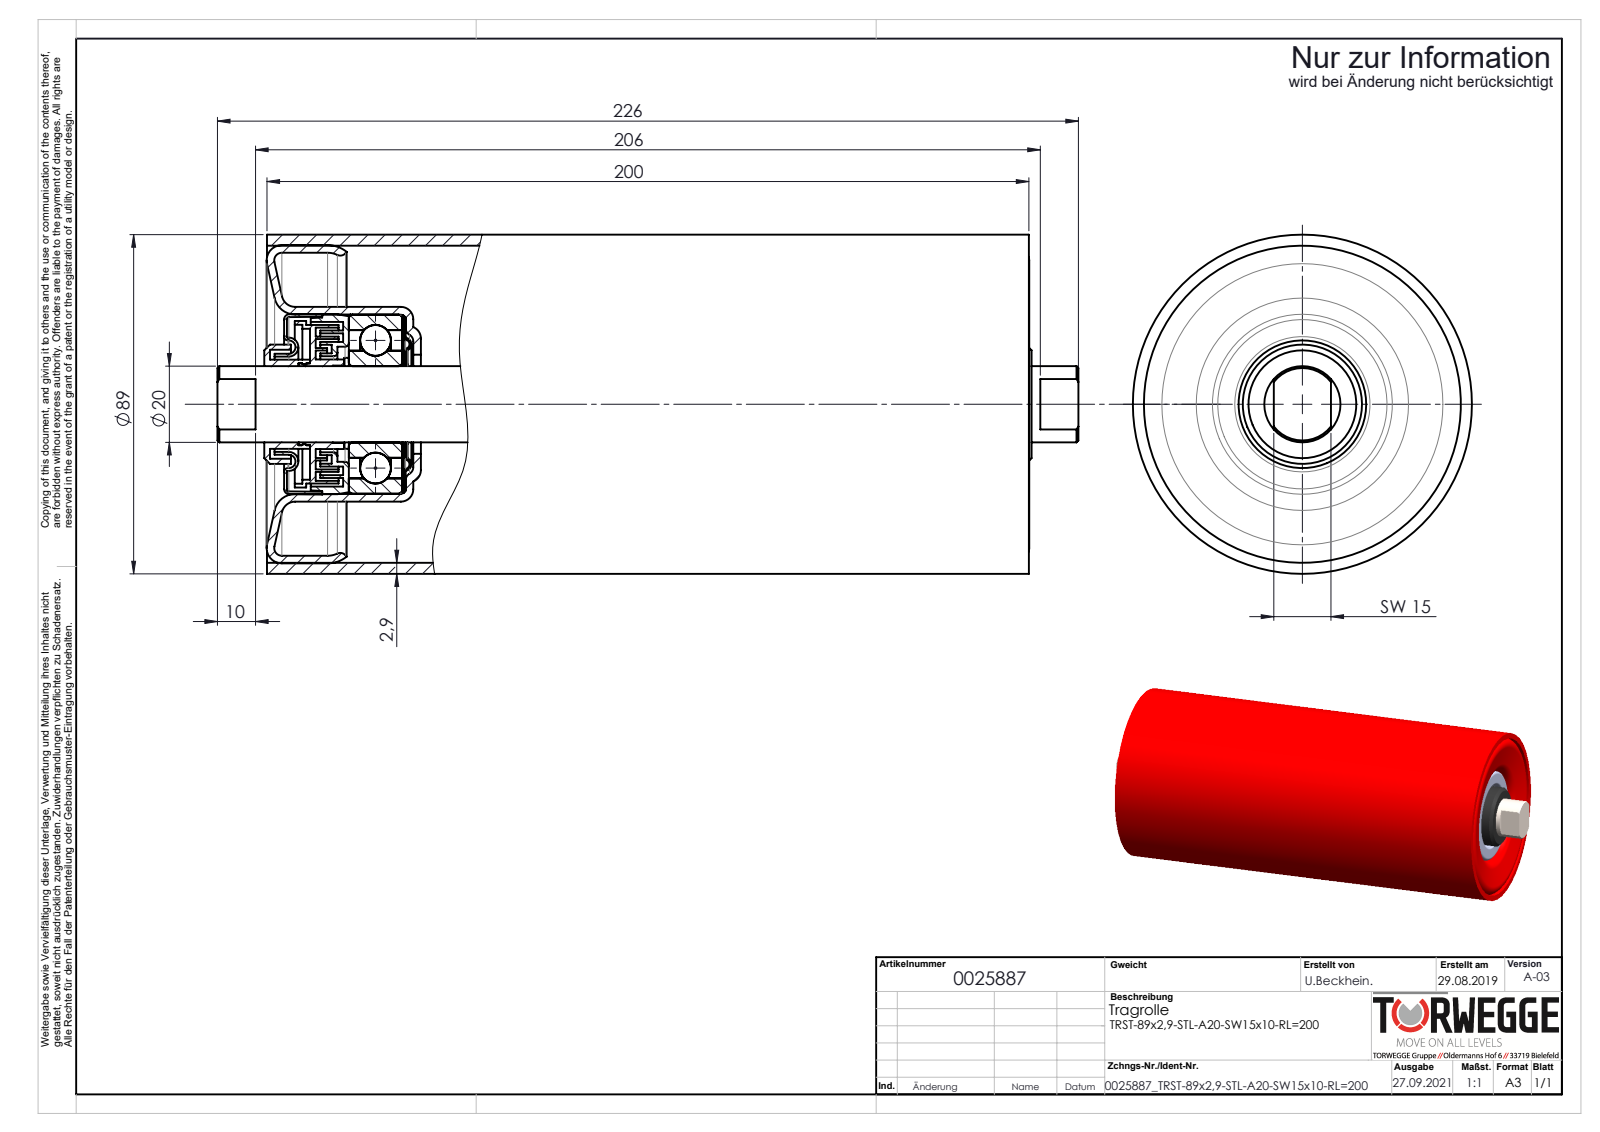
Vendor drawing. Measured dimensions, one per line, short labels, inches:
name: 0025887
written by: SolidWorks 2020 (AUTOMOTIVE_DESIGN)
unit: in
bodies: 24 solids, 606 faces (114 planar, 244 cylindrical, 248 other)
size: 8.898 × 3.504 × 3.504
volume: 23.17 in³; area: 433 in²
holes: 4× ⌀0.079, 1× ⌀0.748, 1× ⌀0.772, 1× ⌀0.787, 1× ⌀0.799, 1× ⌀0.827, 1× ⌀0.846, 1× ⌀0.984, 1× ⌀0.992, 1× ⌀1.024, 1× ⌀1.11, 1× ⌀1.126
bosses: 2× ⌀0.941, 1× ⌀3.504, 1× ⌀3.287, 1× ⌀2.012, 1× ⌀1.858, 1× ⌀1.85, 1× ⌀1.831, 1× ⌀1.72
rounds: 8× R0.079, 1× R0.531
face distances: 0.551, 5.631, 0.587, 5.594, 0.036, 5.043, 6.182, 0.402, 0.953, 0.989
hole spacings: 0.452, 0.453, 0.888, 0.157, 0.157, 0.844, 0.905
